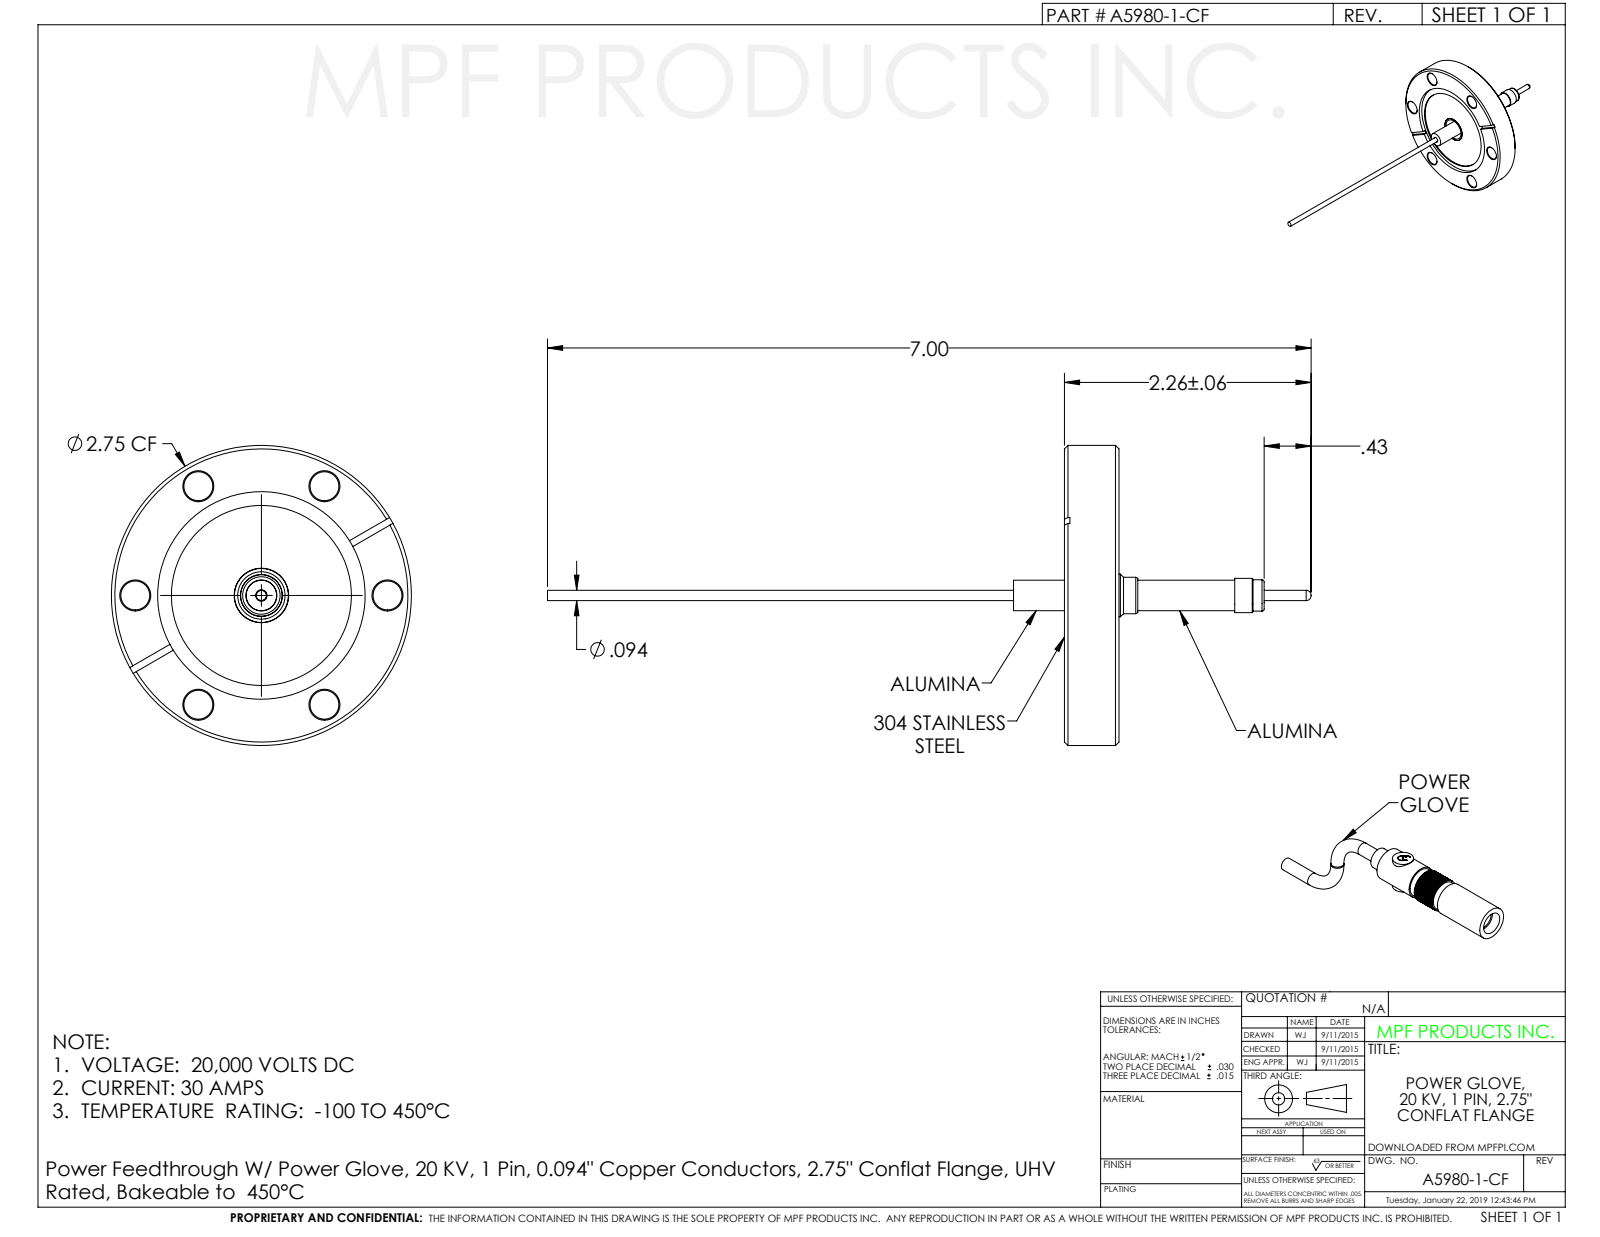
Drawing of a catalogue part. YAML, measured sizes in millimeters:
part_name: "A5980-1-CF"
step_written_by: "SolidWorks 2012 (CONFIG_CONTROL_DESIGN)"
units: millimeters
bodies: {solids: 1, faces: 103, planar: 23, cylindrical: 51, other: 29}
overall_size: [177.8, 69.9, 69.9]
volume: 45290
surface_area: 15670
round_holes:
  - {diameter: 6.7, count: 6}
  - {diameter: 2.7, count: 1}
  - {diameter: 6.6, count: 1}
  - {diameter: 8.7, count: 1}
  - {diameter: 9.8, count: 1}
  - {diameter: 11, count: 1}
  - {diameter: 12.4, count: 1}
  - {diameter: 41.9, count: 1}
  - {diameter: 48.3, count: 1}
round_bosses_or_shafts:
  - {diameter: 69.9, count: 1}
  - {diameter: 9.9, count: 1}
  - {diameter: 9.4, count: 1}
  - {diameter: 7.9, count: 1}
  - {diameter: 7.8, count: 1}
  - {diameter: 7.3, count: 1}
  - {diameter: 7.1, count: 1}
  - {diameter: 2.4, count: 1}
partial_cylinders:
  - {radius: 42, count: 2}
face_to_face_distances: [12.7, 1.3, 11.4, 1.6, 11, 9.7, 1.7, 11.5, 12.8, 22.6]
hole_center_spacings: [29.4, 50.9, 50.9, 58.7, 58.7]
